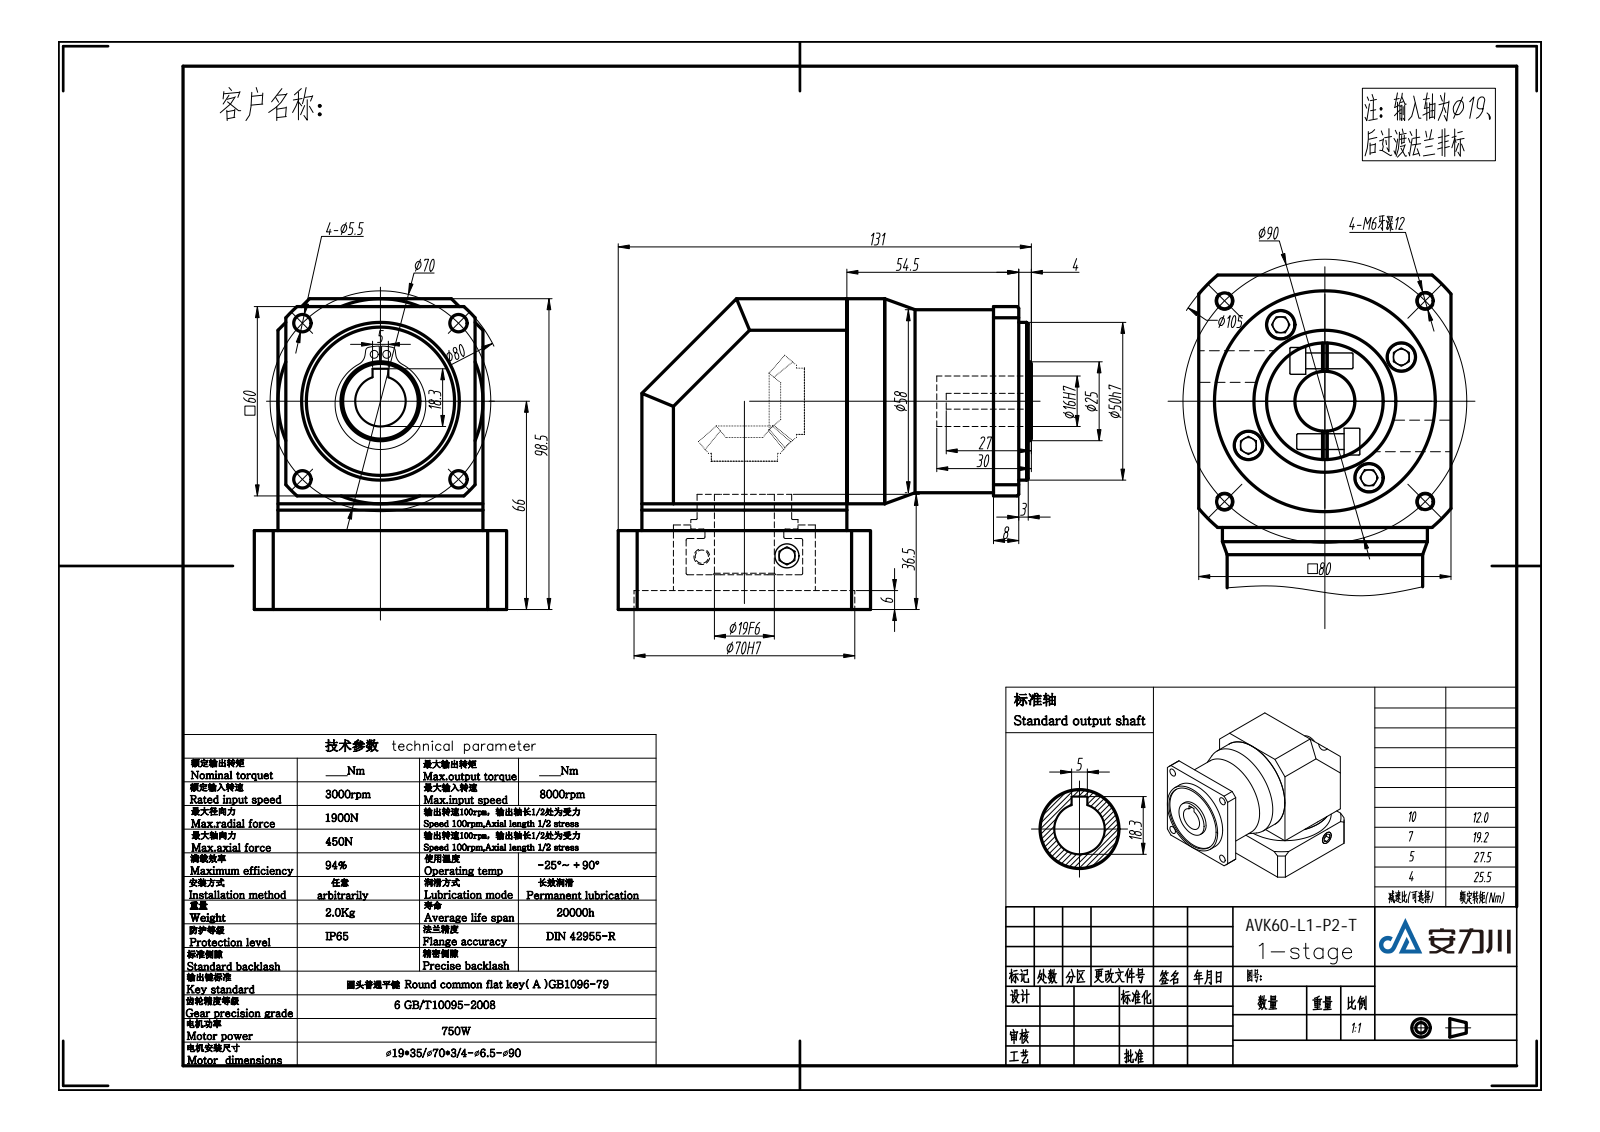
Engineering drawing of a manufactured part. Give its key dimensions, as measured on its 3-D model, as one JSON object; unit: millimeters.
{"part_name": "VGZK60单级模型-T（19-35 70-3 4-6.5-90）", "step_written_by": "SolidWorks 2016 (AUTOMOTIVE_DESIGN)", "units": "millimeters", "bodies": {"solids": 3, "faces": 275, "planar": 155, "cylindrical": 100, "other": 20}, "overall_size": [131, 98.5, 80], "volume_mm3": 527943, "surface_area_mm2": 78005, "round_holes": [[5, 4], [5.5, 4], [9, 4], [10, 4], [8, 2], [16, 1], [19, 1], [20, 1], [45, 1], [47, 1], [70, 1]], "round_bosses_or_shafts": [[8.5, 8], [65, 2], [25, 2], [7.8, 2], [58, 1], [50, 1], [39, 1], [18, 1]], "partial_cylinders_radius": [[40, 1], [52.5, 1]], "face_to_face_distances": [7.5, 72.5, 65, 25.5, 80, 6, 6.5, 25, 8, 11], "hole_center_spacings": [28, 39.6, 44.82, 7, 19.36, 35, 45, 46.44]}
